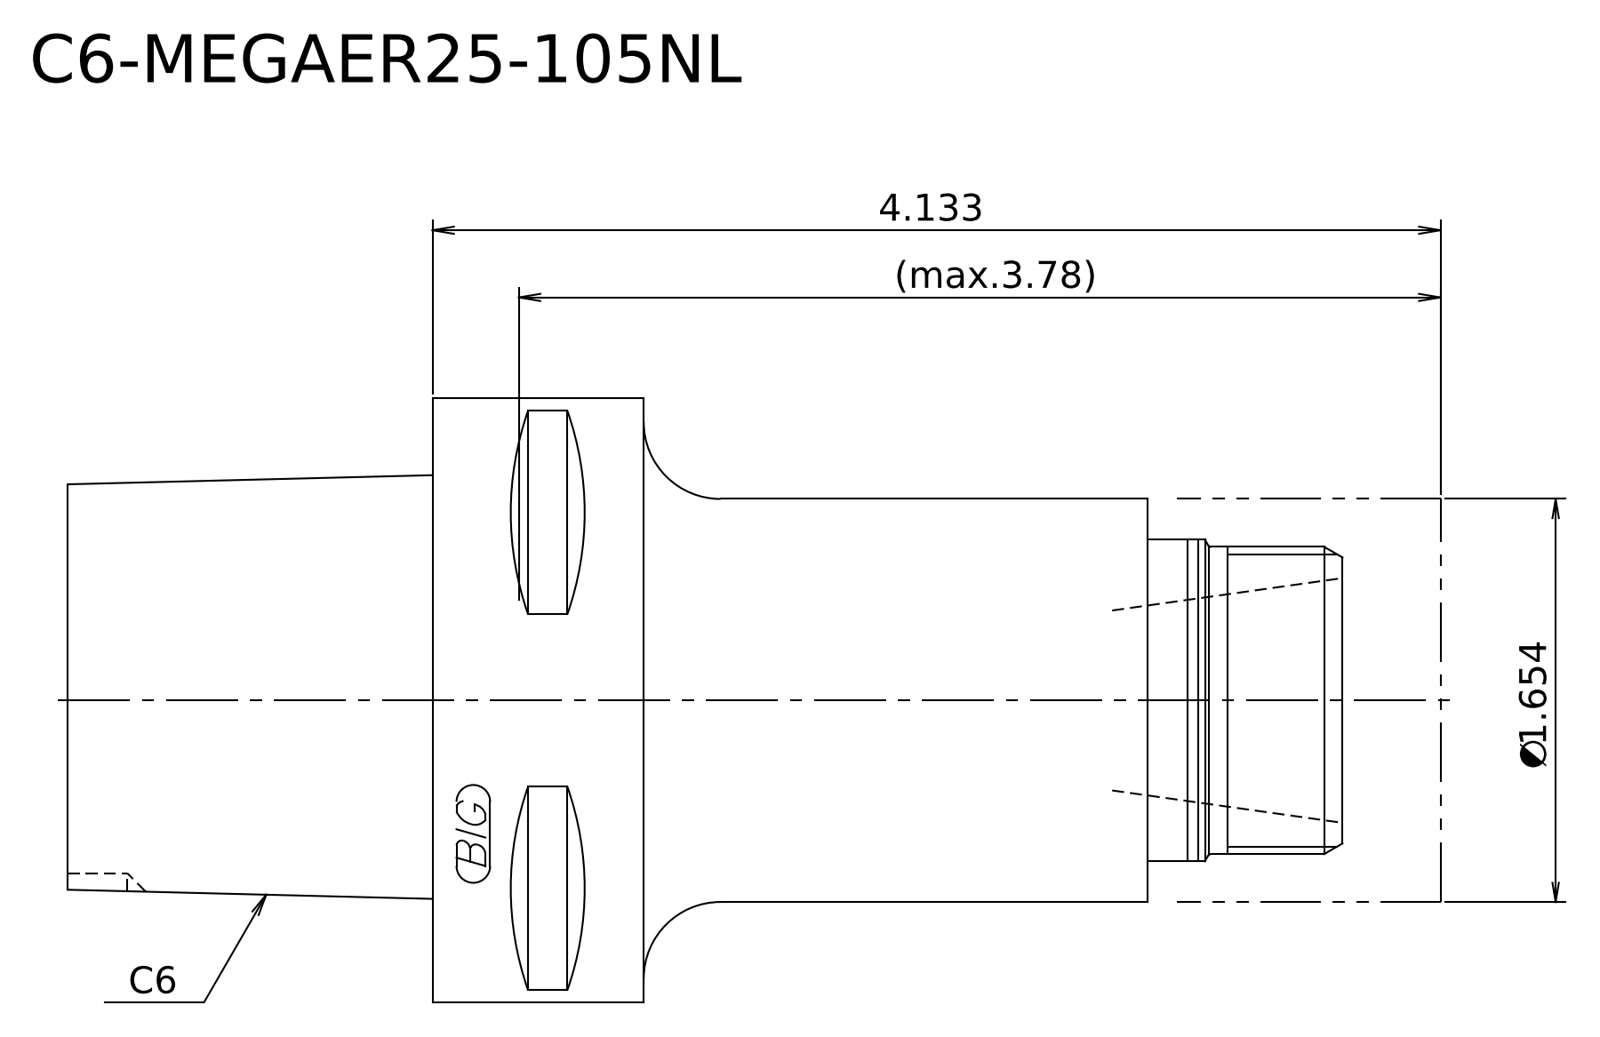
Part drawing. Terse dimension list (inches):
written by: Kubotek KeyCreator 2011 V10.0.2 (22737) (automotive_design)
unit: in
bodies: 2 solids, 18 faces (7 planar, 5 cylindrical, 6 other)
size: 5.63 × 2.48 × 2.48
volume: 15.6 in³; area: 47.06 in²
bosses: 1× ⌀2.48, 1× ⌀1.654, 1× ⌀1.319, 1× ⌀1.26
face distances: 3.051, 1.083, 4.134, 5.63, 4.547, 1.496, 0.402, 0.681, 3.732, 5.228
